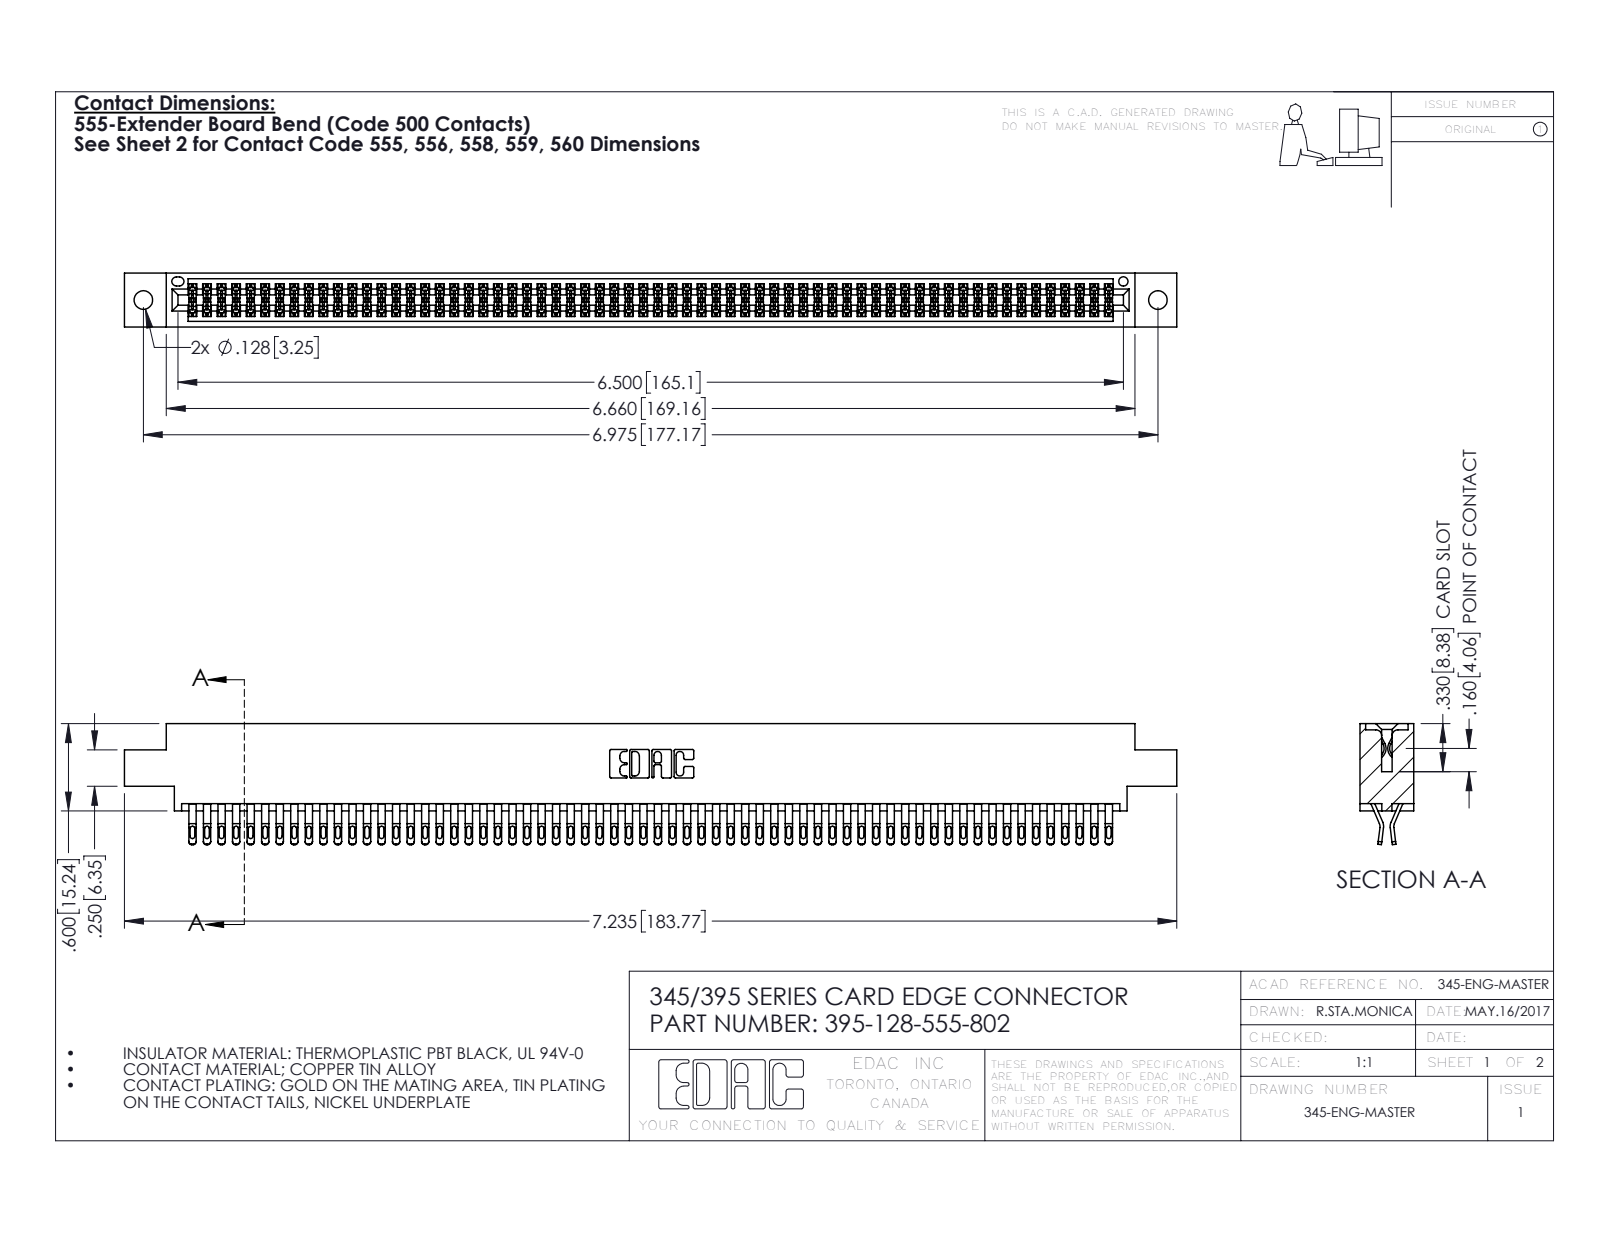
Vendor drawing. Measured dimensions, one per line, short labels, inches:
name: 395-128-555-802; 345-292-001_555 Tail; 345 Part_0.170 Offset - 0.128 Dia
written by: SolidWorks 2016 (CONFIG_CONTROL_DESIGN)
unit: in
bodies: 129 solids, 7298 faces (4052 planar, 3246 cylindrical, 0 other)
size: 7.235 × 0.832 × 0.37
volume: 1.115 in³; area: 44.34 in²
holes: 2× ⌀0.128, 1× ⌀0.064
rounds: 320× R0.016, 256× R0.02, 192× R0.006, 22× R0.01, 6× R0.007, 6× R0.031, 3× R0.026, 2× R0.01
face distances: 0.298, 0.072, 0.37, 0.025, 0.2, 0.098, 0.272, 0.225, 0.175, 0.149
hole spacings: 0.27, 6.739, 6.975
